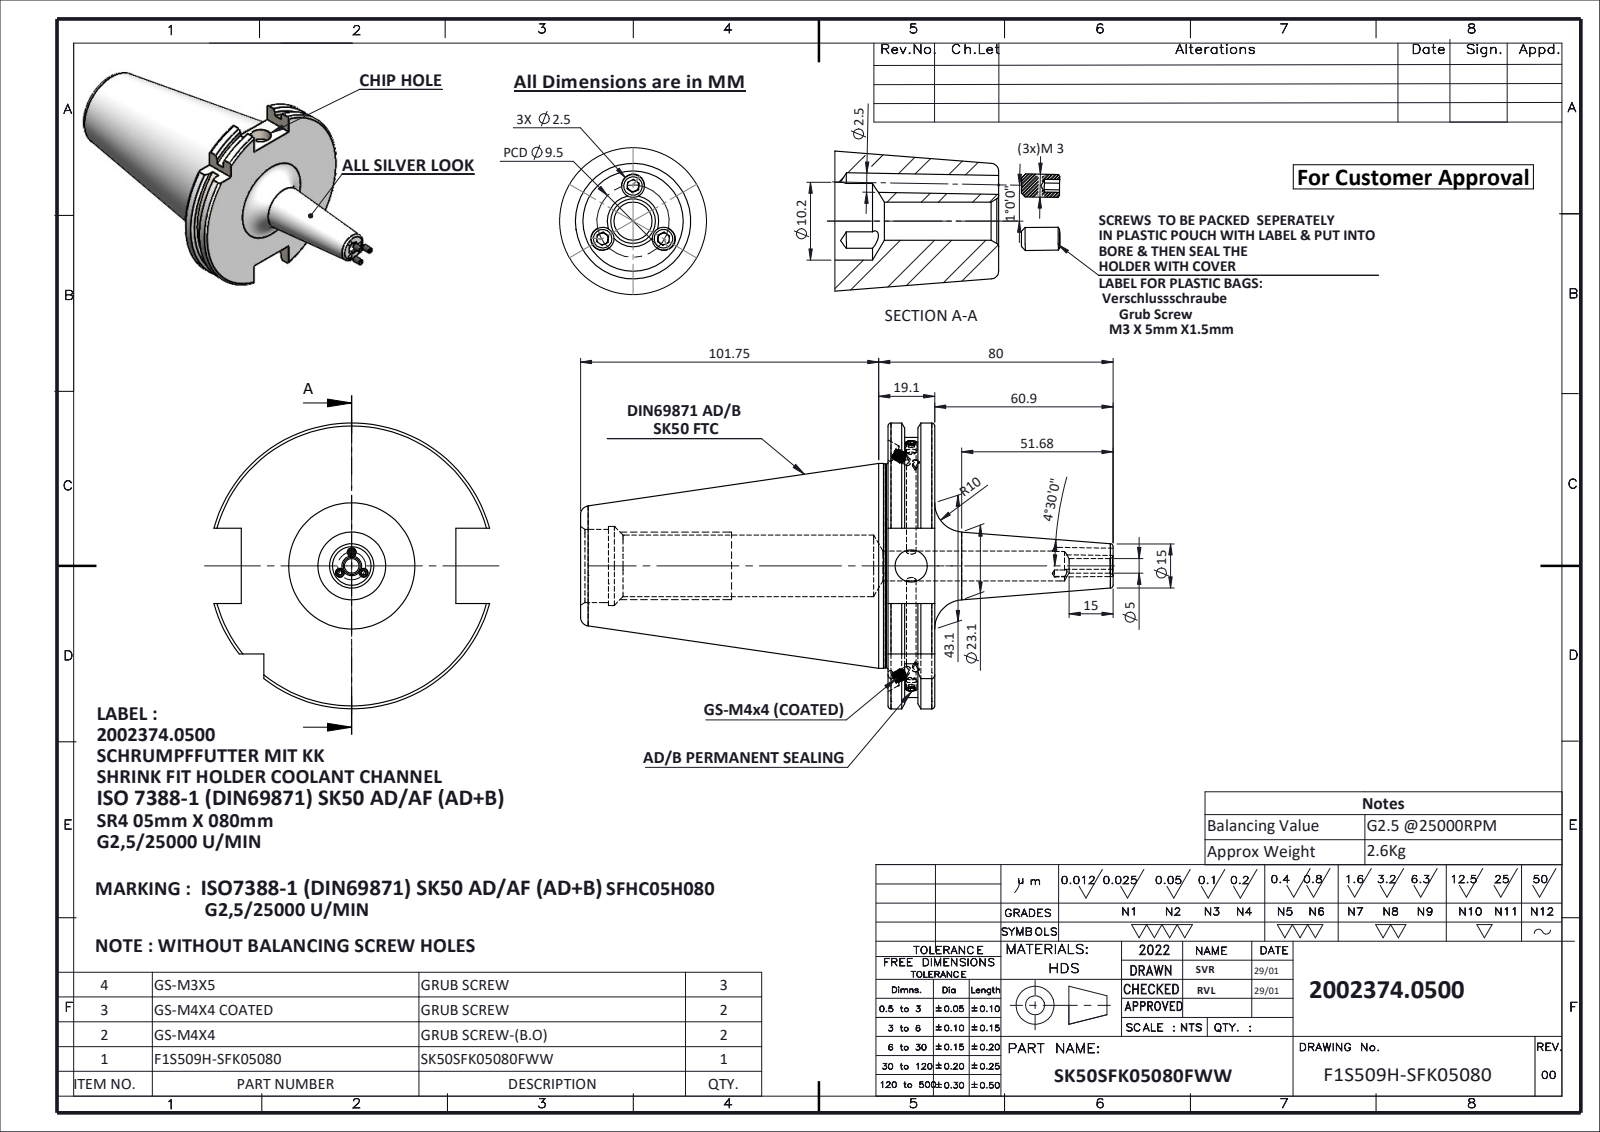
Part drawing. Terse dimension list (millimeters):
name: F1S509H-SFK05080; GS-M4X4-COATING_DIN 913 - M4 x 4-N; SK50SFK05080FWW; GS-M3X5 (+1 more)
written by: SolidWorks 2024 (CONFIG_CONTROL_DESIGN)
unit: mm
bodies: 8 solids, 326 faces (103 planar, 83 cylindrical, 140 other)
size: 189.77 × 97.5 × 94.05
volume: 339 641 mm³; area: 50 611 mm²
holes: 3× ⌀2.5, 2× ⌀3.2, 2× ⌀6, 1× ⌀3.3, 1× ⌀5, 1× ⌀10.2, 1× ⌀11, 1× ⌀21, 1× ⌀25, 1× ⌀27
bosses: 4× ⌀4, 3× ⌀3, 2× ⌀2.9, 1× ⌀69.85, 1× ⌀69.45
rounds: 1× R44.9, 1× R48.75
face distances: 15.9, 5.66, 10.24, 10.14, 4.48, 5.76, 104.95, 110.61, 115.09, 120.85
